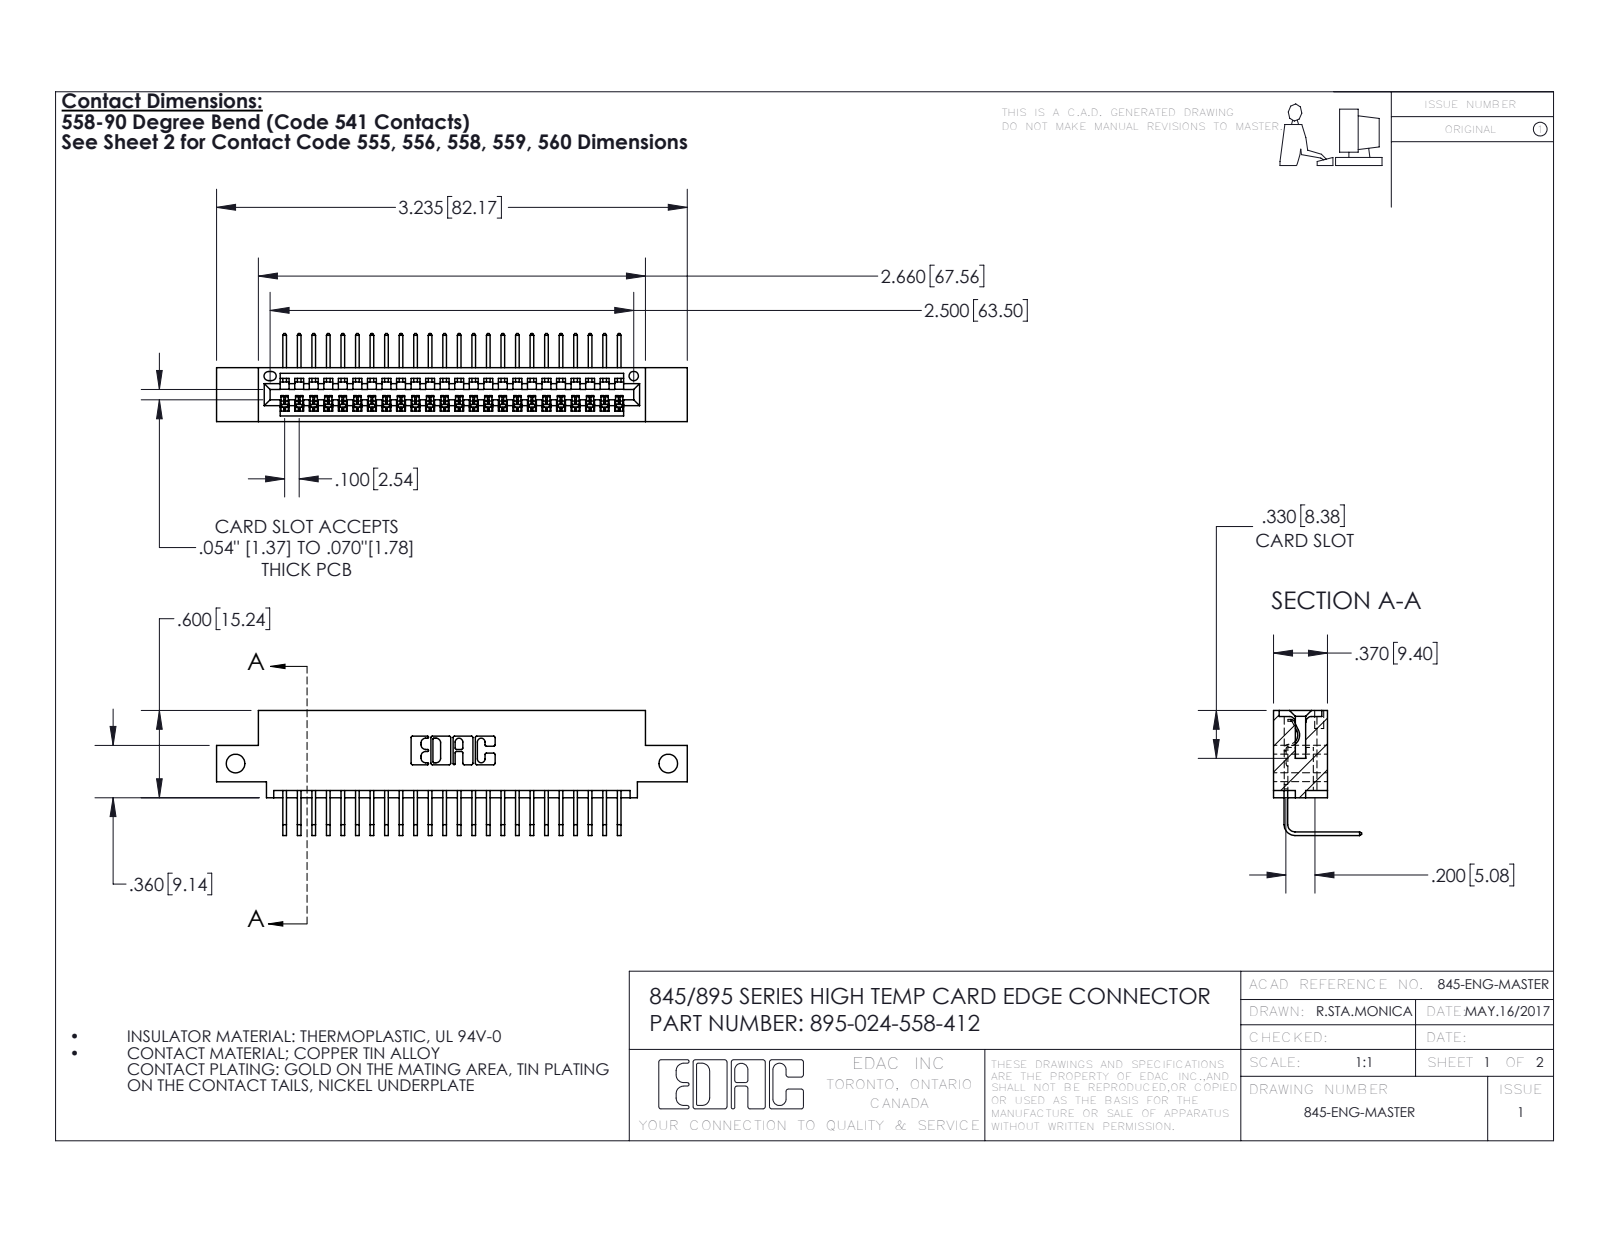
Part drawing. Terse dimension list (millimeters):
name: 345-292-001_558 Tail - 2; 345 Part_0.110 Offset - Side Mount; 395-024-558-412
written by: SolidWorks 2016 (CONFIG_CONTROL_DESIGN)
unit: mm
bodies: 25 solids, 1570 faces (1092 planar, 478 cylindrical, 0 other)
size: 82.2 × 21.8 × 15.4
volume: 7 570 mm³; area: 10 230 mm²
holes: 2× ⌀3.3, 1× ⌀1.6
rounds: 48× R0.2, 22× R0.3, 6× R0.2, 6× R0.8, 3× R0.7, 2× R0.8, 2× R1, 1× R0.4
face distances: 1.8, 7.6, 9.4, 5.1, 2.5, 6.9, 0.6, 5.7, 3.8, 1.8
hole spacings: 75.6
